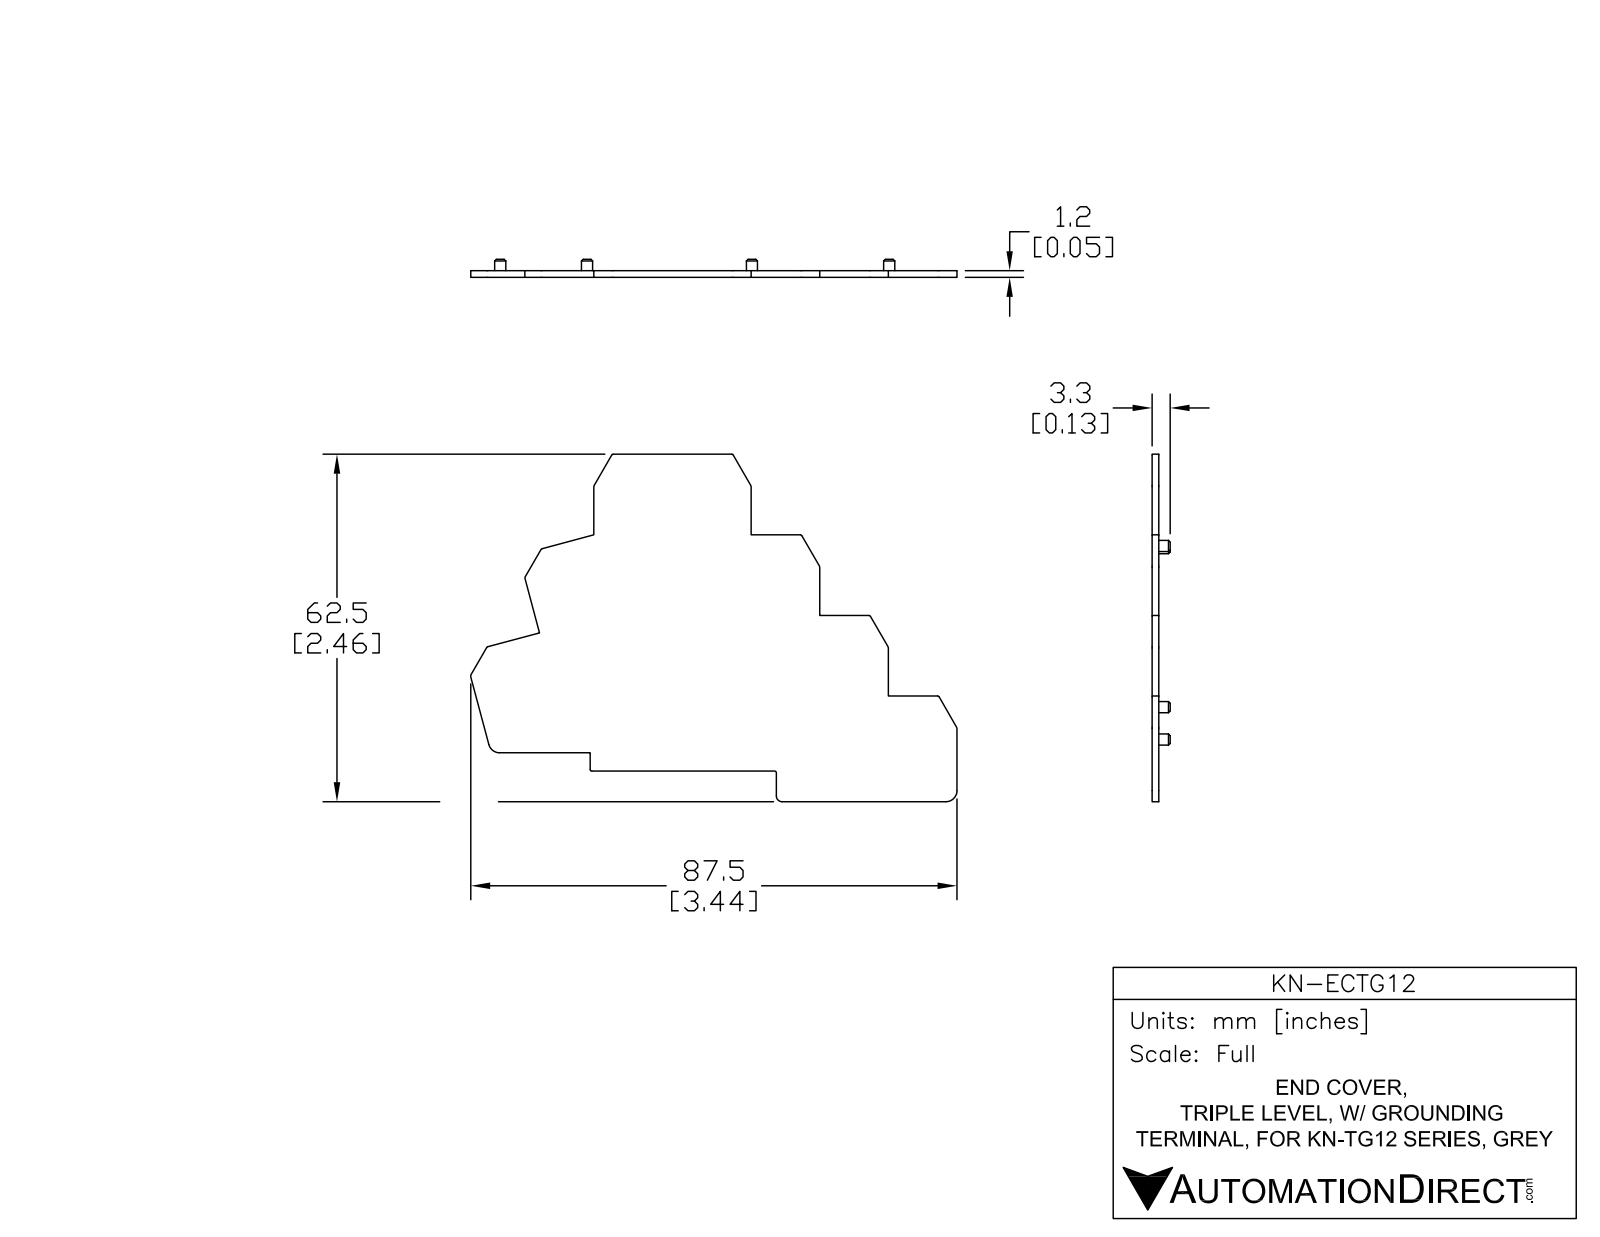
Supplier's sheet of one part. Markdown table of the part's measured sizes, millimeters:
| quantity | value |
| --- | --- |
| part name | KN-ECTG12 |
| STEP written by | SolidWorks 2014 (AUTOMOTIVE_DESIGN) |
| units | millimeters |
| bodies | 1 solid, 76 faces (32 planar, 36 cylindrical, 8 other) |
| overall size | 87.5 × 62.5 × 3.25 |
| volume | 4 077 mm³ |
| surface area | 7 189 mm² |
| round holes (diameter × count) | 1.4 × 4 |
| round bosses / shafts (diameter × count) | 2 × 4 |
| partial cylindrical surfaces (radius × count) | 0.3 × 11, 0.5 × 5, 2 × 2, 1 × 1 |
| main face-to-face distances | 1.2, 14.5, 5.5, 24.7, 12.35, 62.5, 57, 29, 8.8, 3.3 |
| hole center spacings | 29.68, 37.8, 38.09, 57.14, 61.44, 70.24 |
